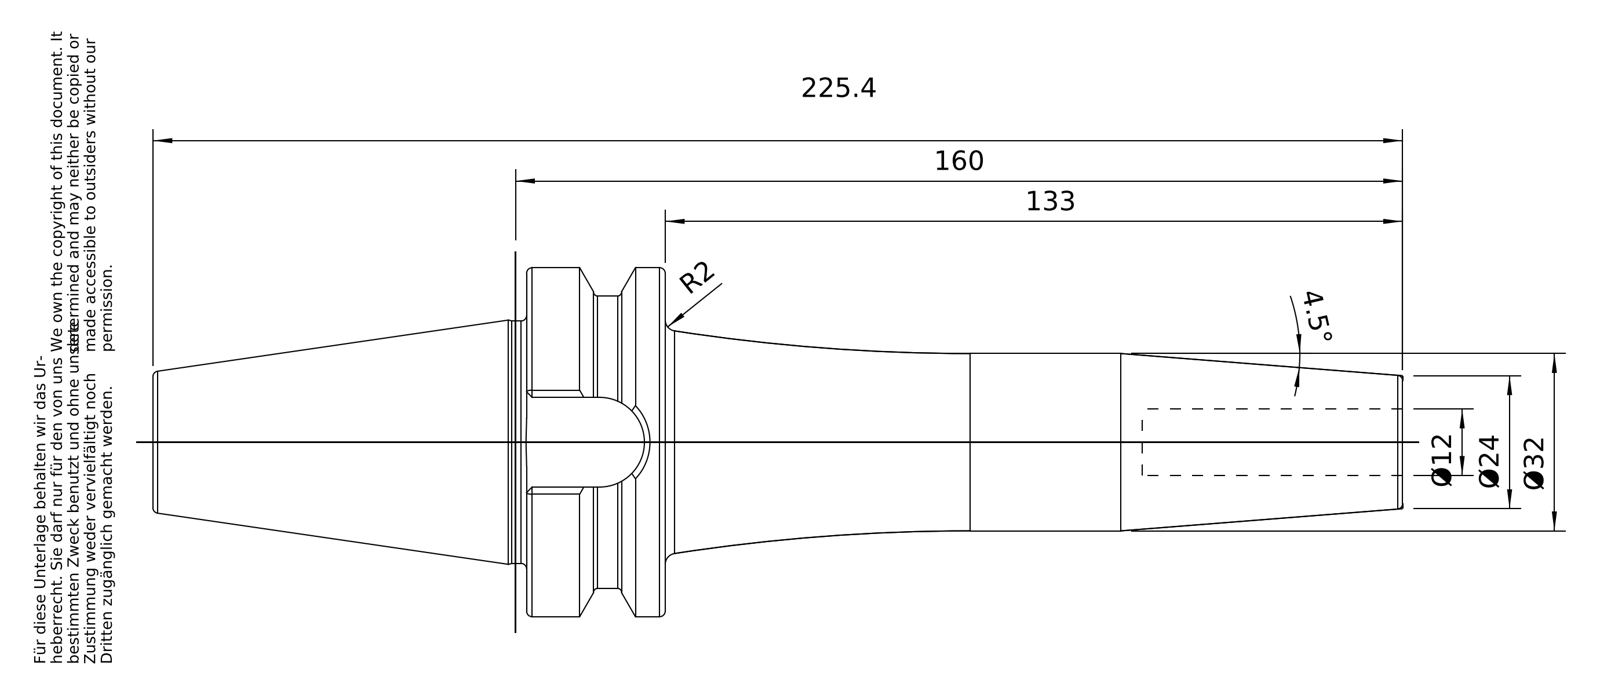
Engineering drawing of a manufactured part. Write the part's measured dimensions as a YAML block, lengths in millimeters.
part_name: "40-642-12"
step_written_by: "PRO/ENGINEER BY PARAMETRIC TECHNOLOGY CORPORATION, 2010430 (CONFIG_CONTROL_DESIGN)"
units: millimeters
bodies: {solids: 1, faces: 98, planar: 26, cylindrical: 22, other: 50}
overall_size: [225.4, 62.98, 62.98]
volume: 227133
surface_area: 35928
round_holes:
  - {diameter: 12, count: 1}
  - {diameter: 13.84, count: 1}
  - {diameter: 17.01, count: 1}
  - {diameter: 17.5, count: 1}
round_bosses_or_shafts:
  - {diameter: 62.98, count: 1}
  - {diameter: 52.75, count: 1}
  - {diameter: 43.75, count: 1}
  - {diameter: 32, count: 1}
  - {diameter: 16.01, count: 1}
partial_cylinders:
  - {radius: 8.1, count: 1}
face_to_face_distances: [25, 44.9, 158, 133, 16.2, 67.4, 92.4, 225.4, 178.4, 111]
